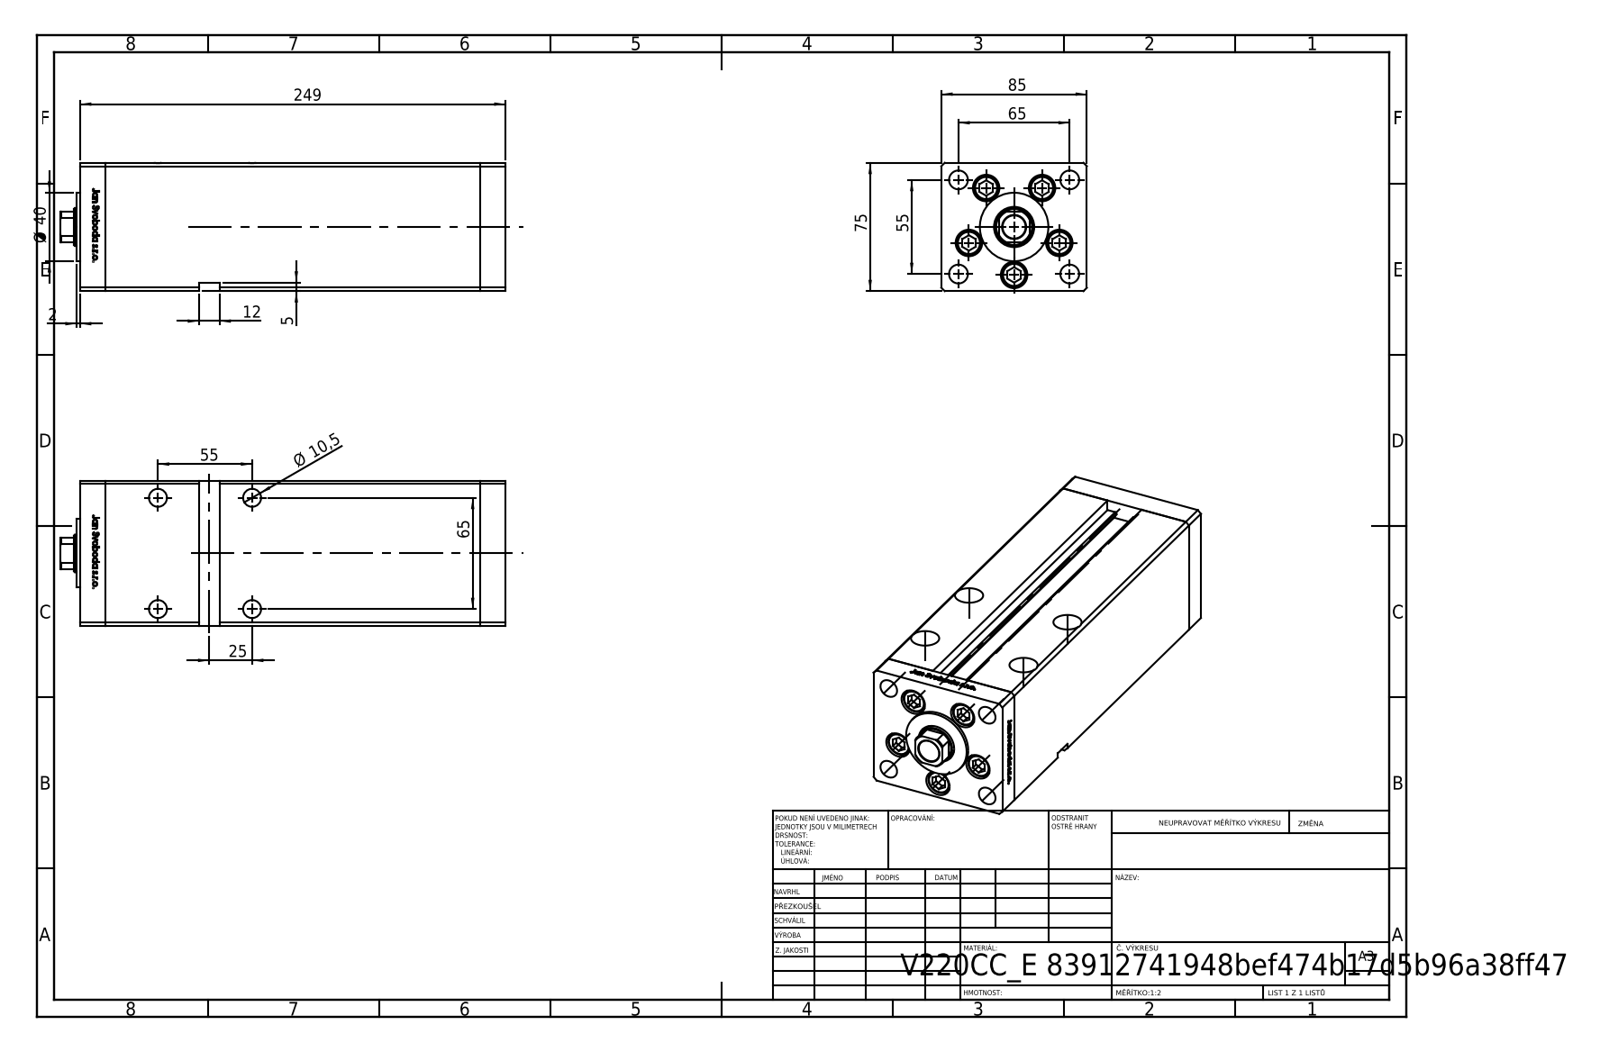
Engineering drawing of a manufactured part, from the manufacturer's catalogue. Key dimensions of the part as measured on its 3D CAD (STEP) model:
Part name (STEP PRODUCT): V220C_VC_E; V220C_FRONT_E; ALLEN BOLT; V220C_E MIDDLE (+1 more)
STEP written by: SolidWorks 2019 (CONFIG_CONTROL_DESIGN)
Units: millimetres
Bodies: 14 solids, 1212 faces (473 planar, 165 cylindrical, 574 other)
Overall size (bounding box): 260 × 85 × 75
Volume: 1 341 000 mm³ · Surface area: 209 531 mm²
Round holes (diameter × count): ⌀11 ×9, ⌀15.5 ×5, ⌀10.5 ×4, ⌀16.5 ×4, ⌀2 ×2, ⌀13.16 ×2, ⌀13.5 ×1, ⌀22 ×1, ⌀23.5 ×1
Round bosses / shafts (diameter × count): ⌀14.5 ×5, ⌀8 ×5, ⌀40 ×1
Partial cylindrical surfaces — rounded edges, fillets, slot ends (radius × count): R0.93 ×2, R10.5 ×1
Main face-to-face distances: 85, 75, 15, 218.5, 233.5, 248.5, 68.5, 10.5, 34.25, 64.5
Hole centre spacings: 28, 42.57, 55, 65, 85.15, 16.86, 19.17, 32.33
